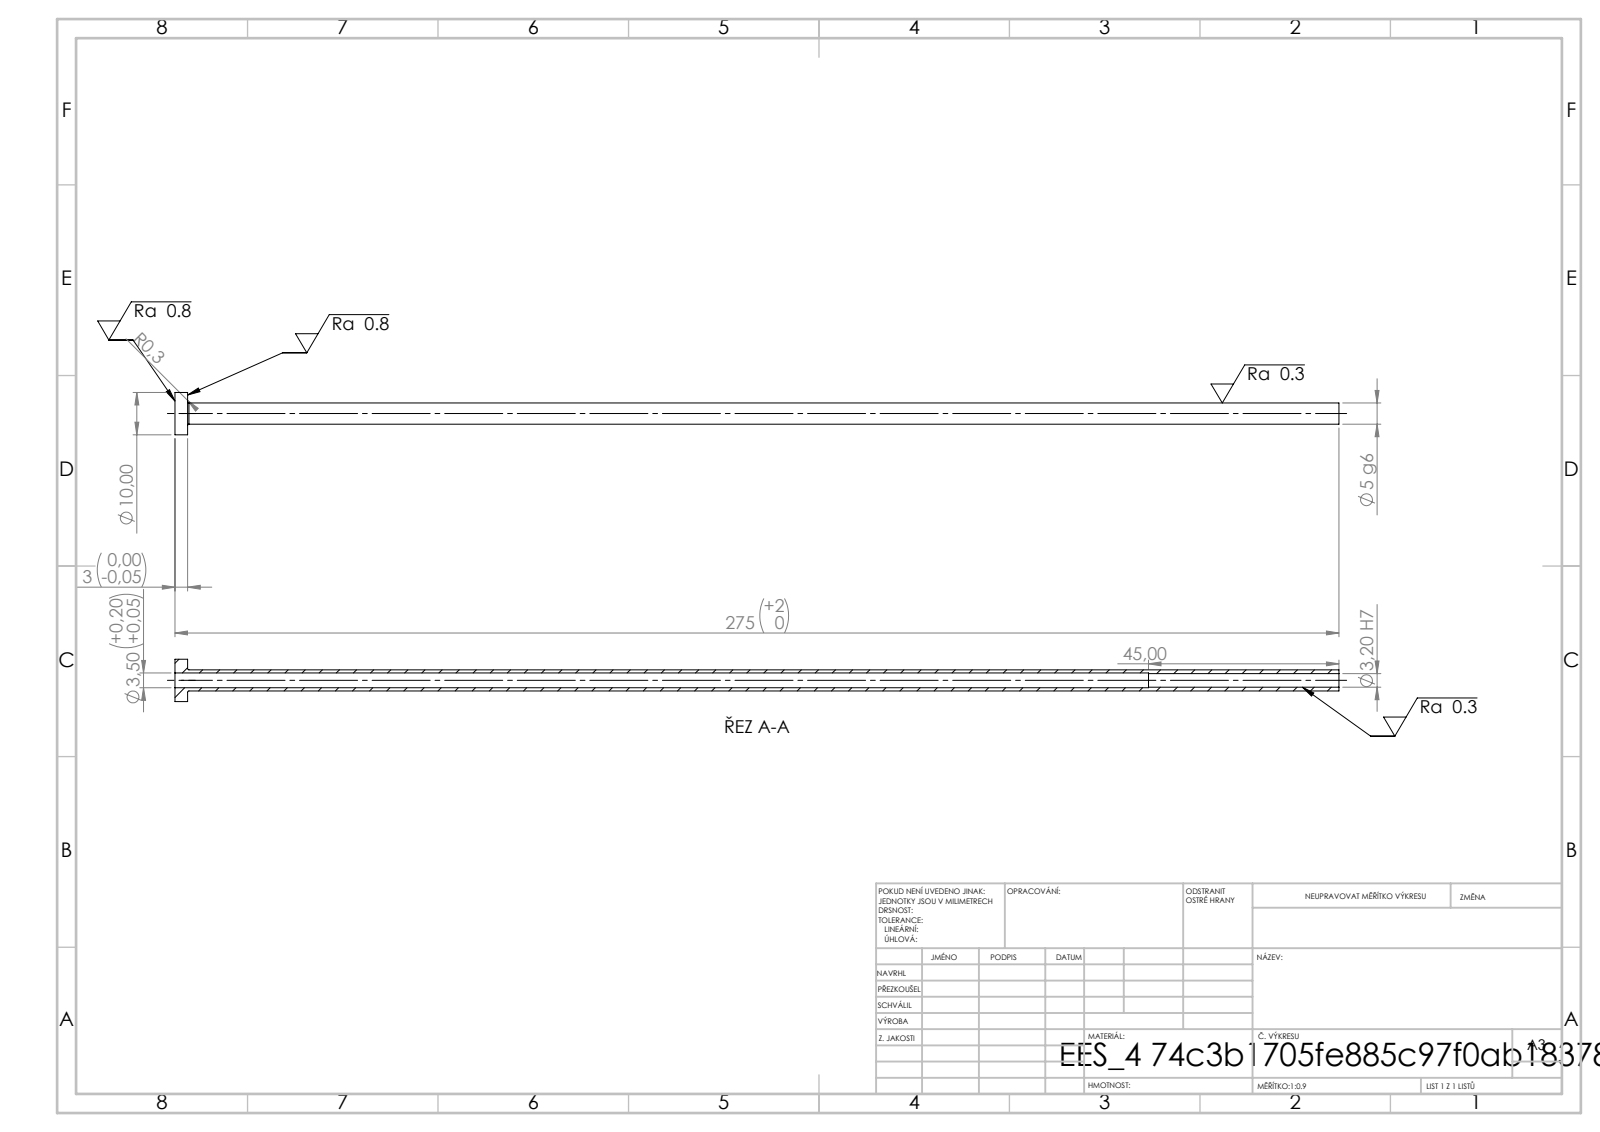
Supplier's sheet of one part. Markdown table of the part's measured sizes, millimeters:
| quantity | value |
| --- | --- |
| STEP written by | SolidWorks 2019 (CONFIG_CONTROL_DESIGN) |
| units | millimeters |
| bodies | 1 solid, 14 faces (4 planar, 8 cylindrical, 2 other) |
| overall size | 275 × 10 × 10 |
| volume | 3 002 mm³ |
| surface area | 7 487 mm² |
| round holes (diameter × count) | 3.2 × 1, 3.5 × 1 |
| round bosses / shafts (diameter × count) | 10 × 1, 5 × 1 |
| main face-to-face distances | 3, 275, 272, 230, 227, 45 |
